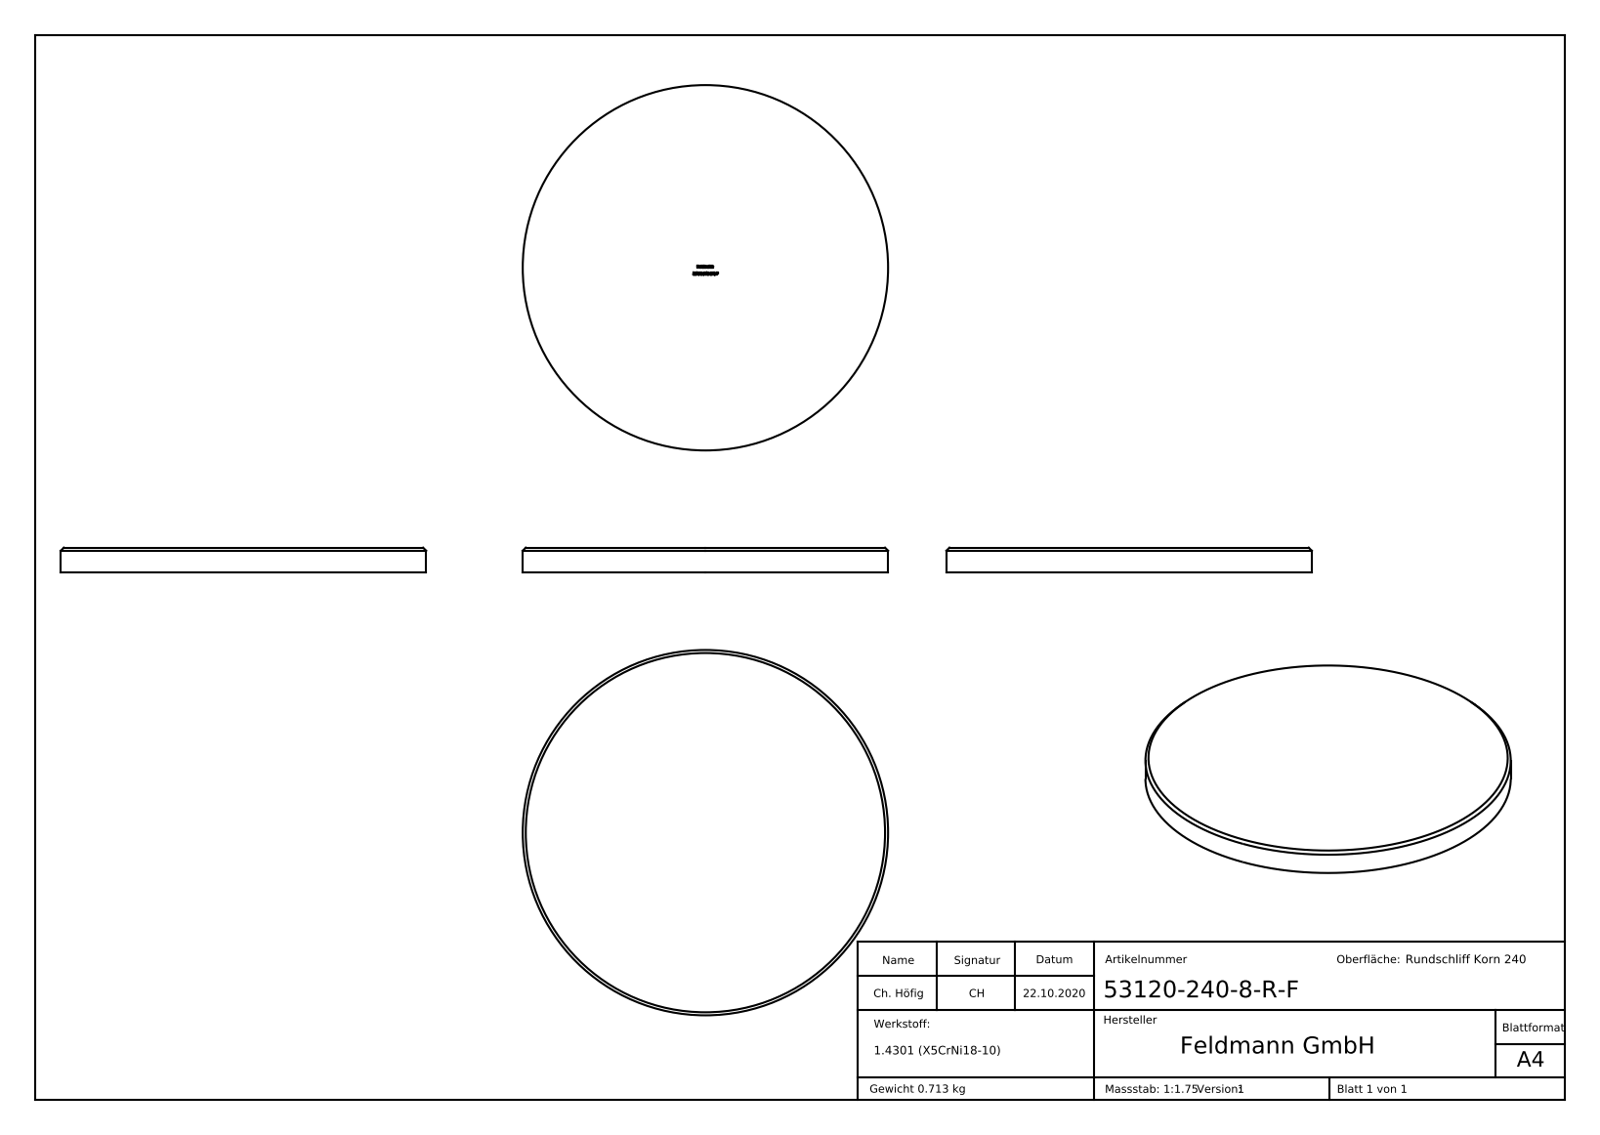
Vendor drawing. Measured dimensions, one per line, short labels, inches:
name: 53120-240-8-R-F
written by: SolidWorks 2018 (CONFIG_CONTROL_DESIGN)
unit: in
bodies: 1 solid, 291 faces (165 planar, 2 cylindrical, 124 other)
size: 4.724 × 4.724 × 0.315
volume: 5.51 in³; area: 39.4 in²
bosses: 1× ⌀4.724
face distances: 0.315, 0.311, 0.088, 0.048, 0.157, 0.115, 0.028, 0.018, 0.092, 0.091
